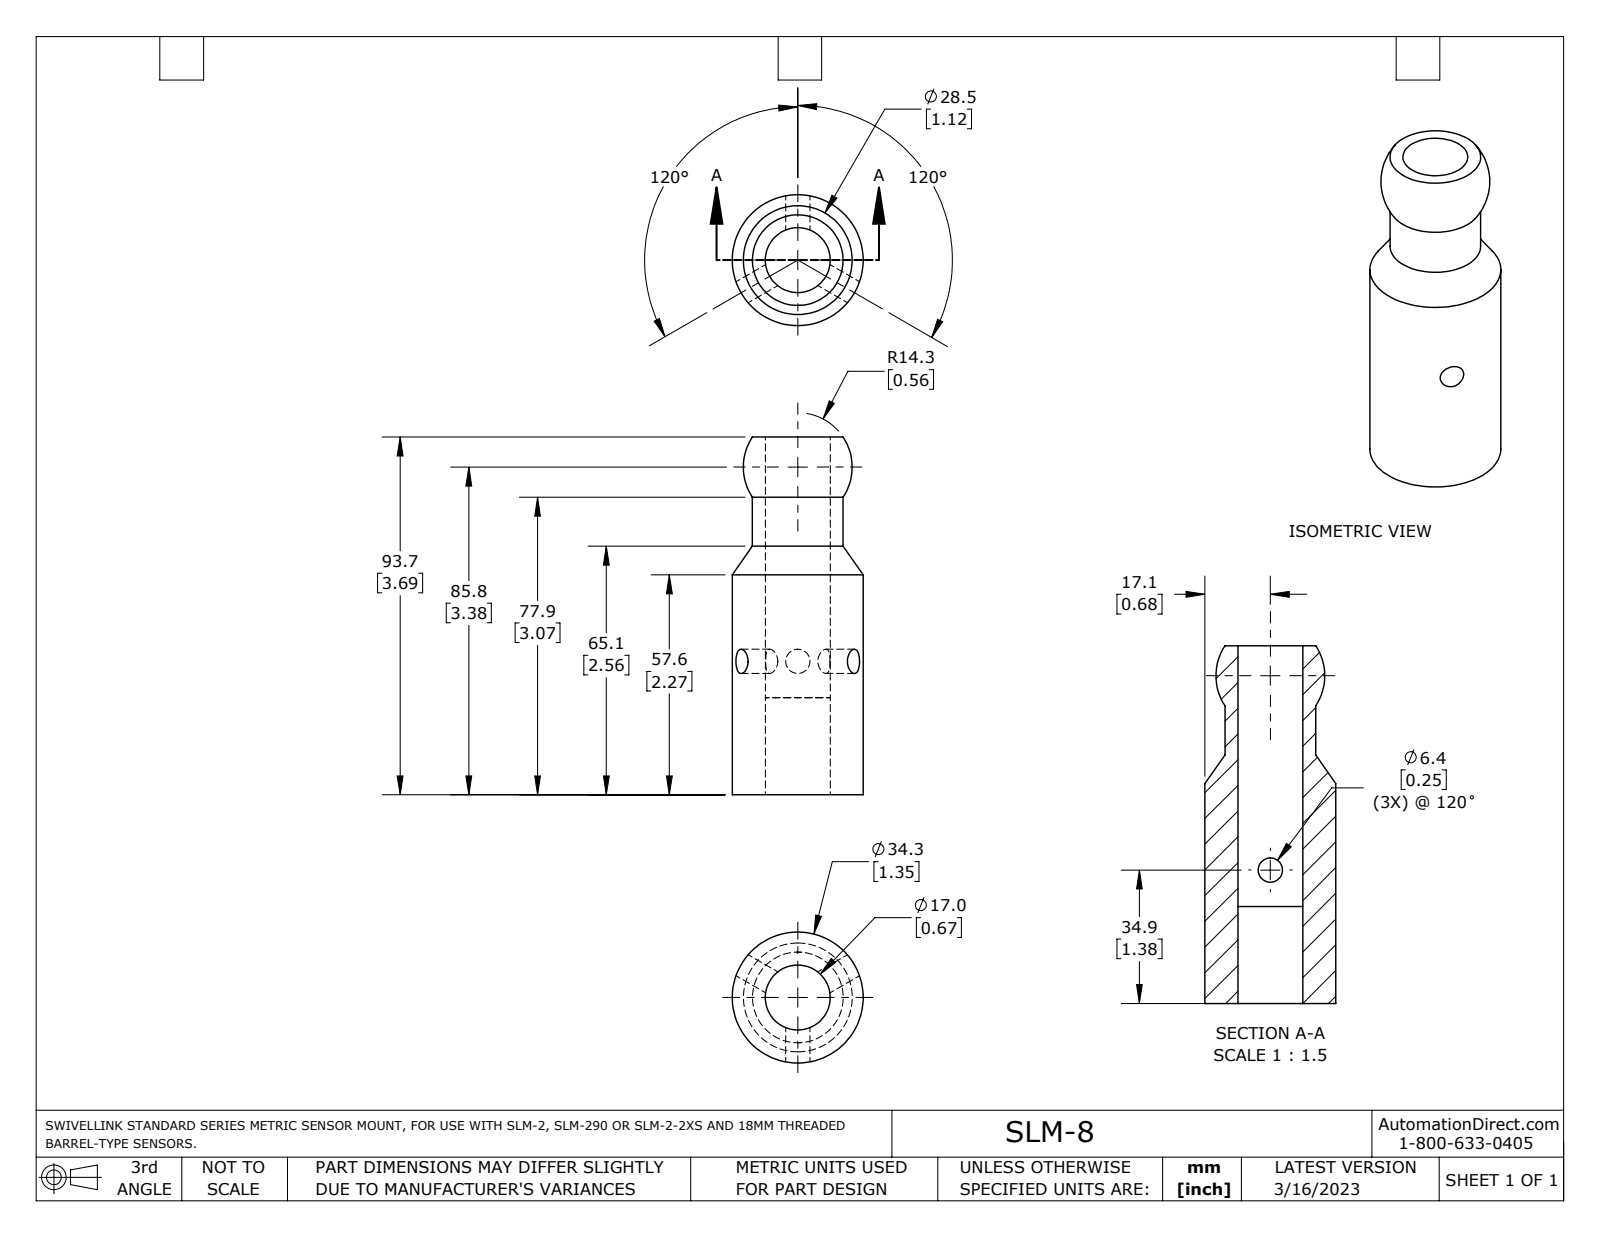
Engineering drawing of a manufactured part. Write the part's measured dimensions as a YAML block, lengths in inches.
part_name: "SLM-8"
step_written_by: "SolidWorks 2021 (AUTOMOTIVE_DESIGN)"
units: inches
bodies: {solids: 1, faces: 12, planar: 2, cylindrical: 7, other: 3}
overall_size: [3.939, 1.35, 1.35]
volume: 2.361
surface_area: 23.85
round_holes:
  - {diameter: 0.25, count: 3}
  - {diameter: 0.669, count: 1}
round_bosses_or_shafts:
  - {diameter: 1.35, count: 1}
  - {diameter: 0.935, count: 1}
face_to_face_distances: [3.687]
